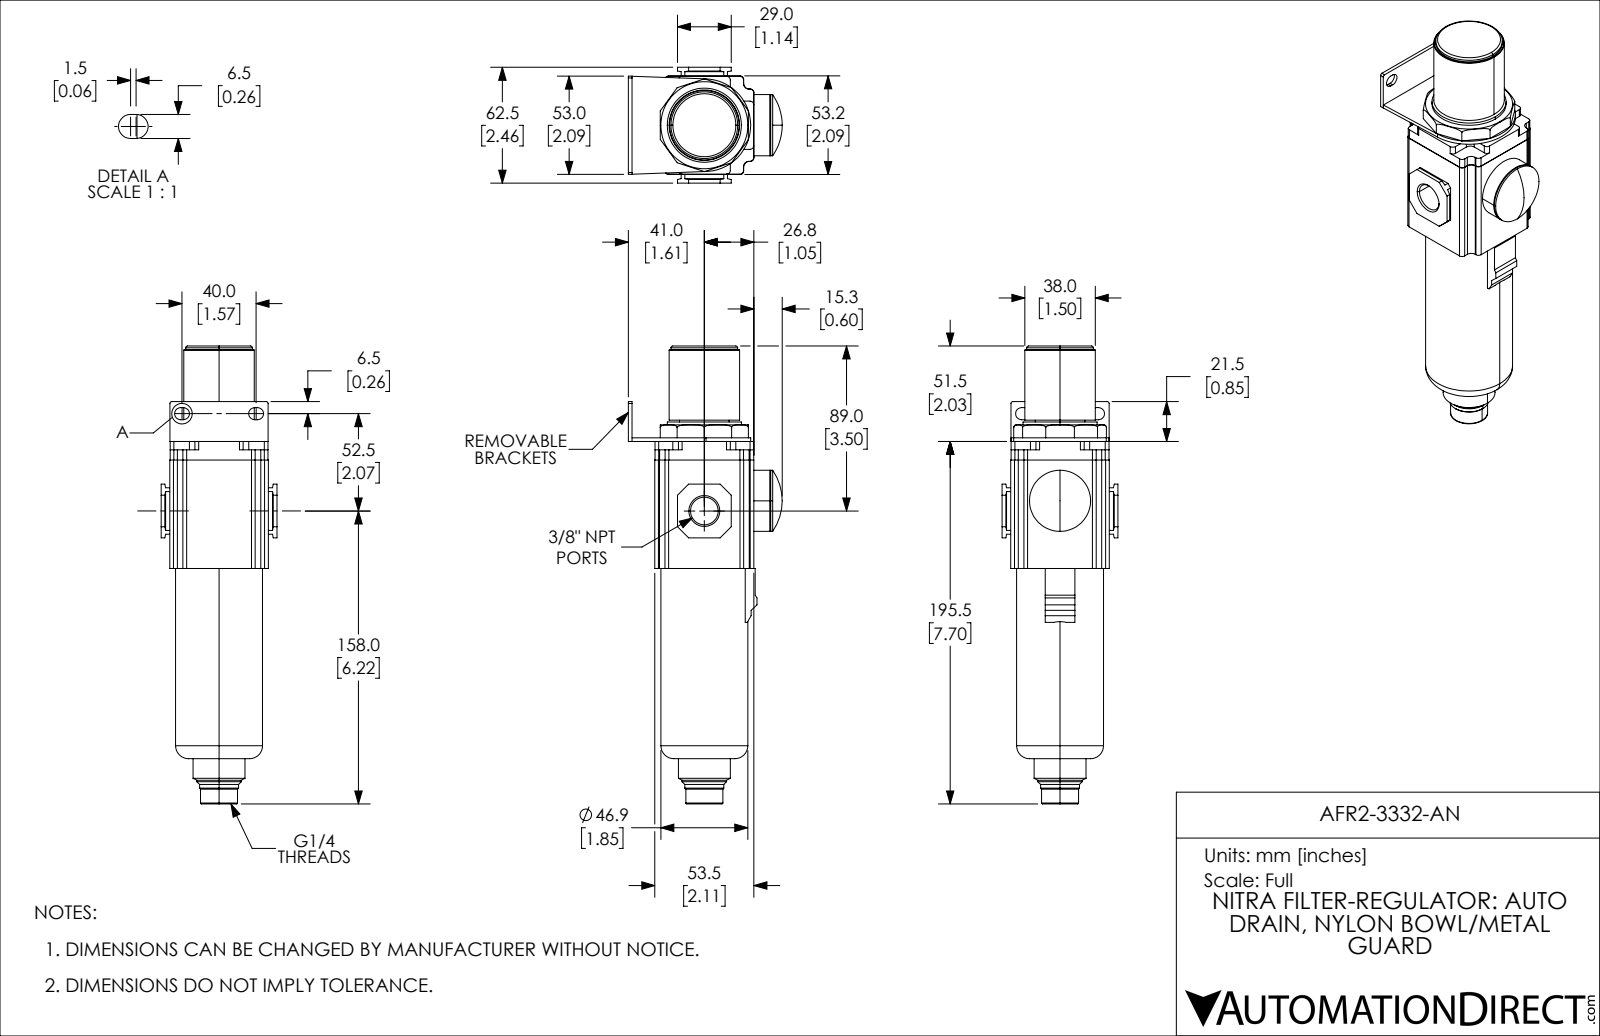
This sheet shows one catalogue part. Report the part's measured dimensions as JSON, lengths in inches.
{"part_name": "AFR2-3332-AN", "step_written_by": "SolidWorks 2019 (CONFIG_CONTROL_DESIGN)", "units": "inches", "bodies": {"solids": 1, "faces": 221, "planar": 124, "cylindrical": 71, "other": 26}, "overall_size": [9.724, 3.269, 2.461], "volume_in3": 27.43, "surface_area_in2": 80.97, "round_holes": [[0.451, 1], [0.589, 1]], "round_bosses_or_shafts": [[1.846, 1], [1.575, 1], [1.496, 1], [1.417, 1], [1.299, 1], [1.102, 1], [1.054, 1], [0.945, 1]], "partial_cylinders_radius": [[0.079, 24], [0.118, 12], [0.128, 4], [0.039, 2], [0.984, 1]], "face_to_face_distances": [0.079, 2.094, 2.106, 0.561, 0.183, 2.278, 0.482, 2.667, 2.028, 1.949]}
